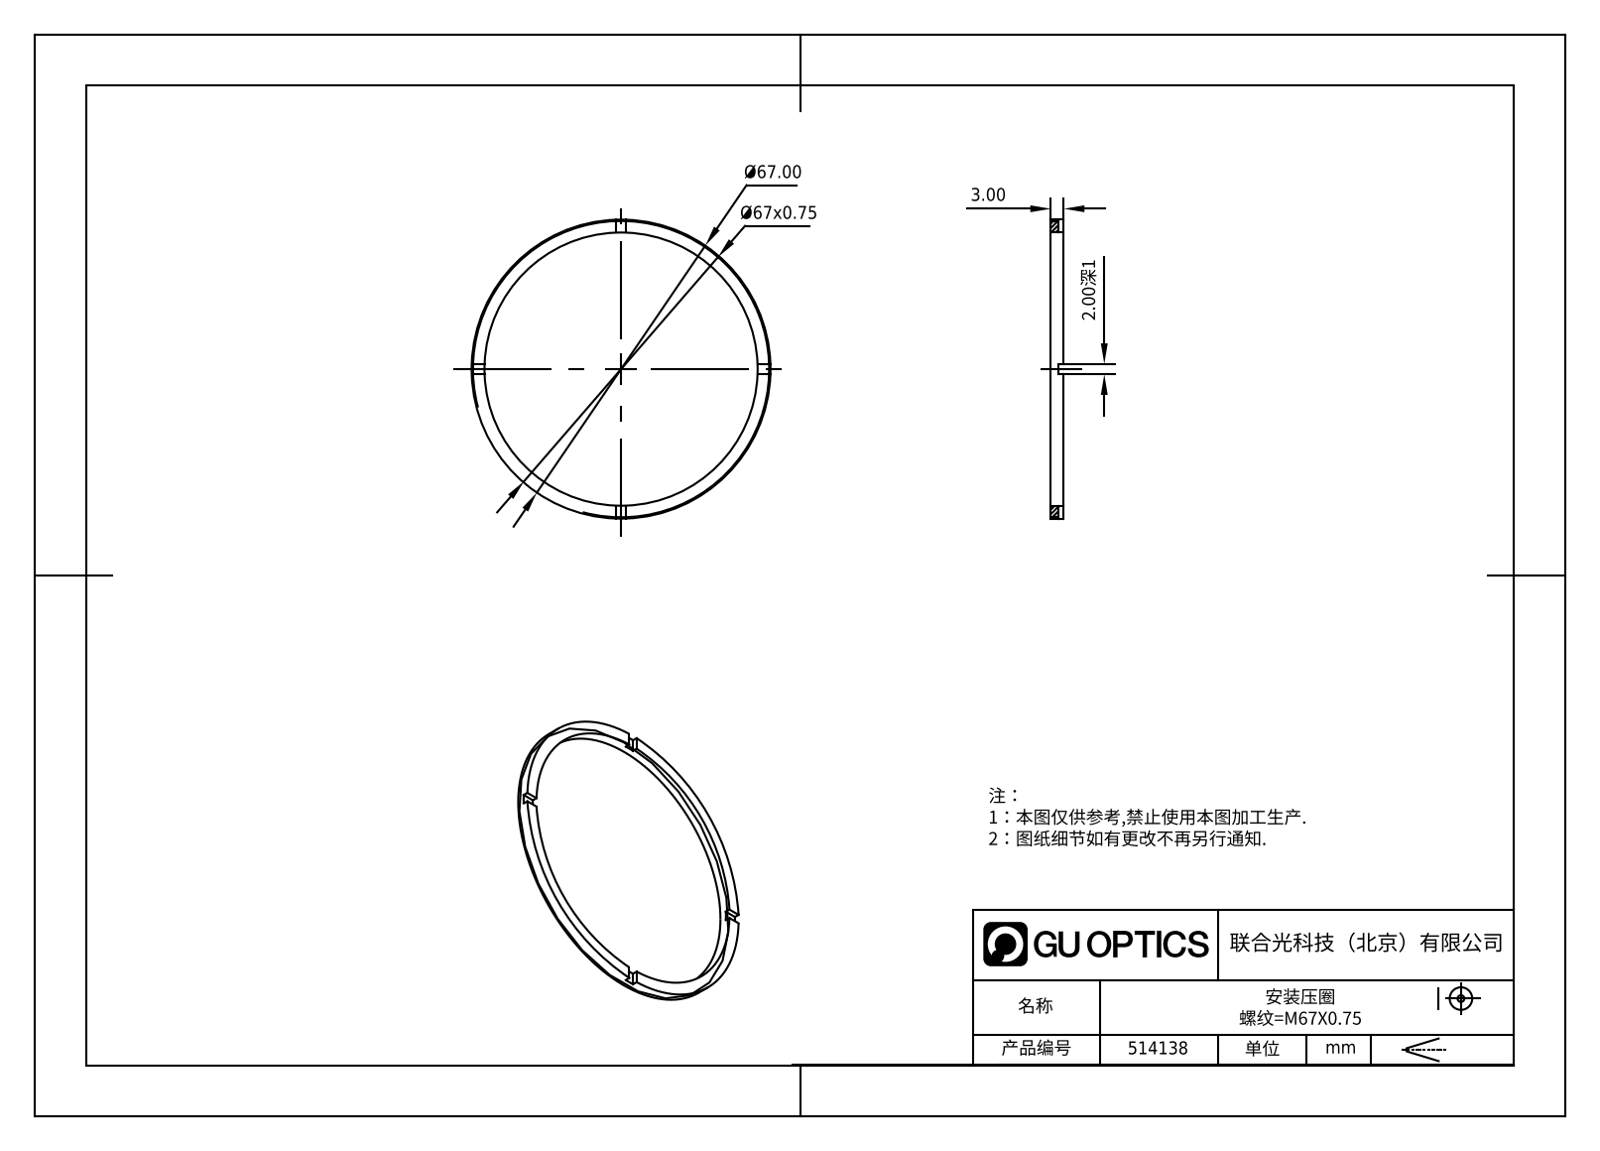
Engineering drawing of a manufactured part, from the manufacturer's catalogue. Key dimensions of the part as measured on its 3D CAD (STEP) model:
Part name (STEP PRODUCT): 514138
STEP written by: SolidWorks 2020 (CONFIG_CONTROL_DESIGN)
Units: millimetres
Bodies: 1 solid, 21 faces (17 planar, 4 cylindrical, 0 other)
Overall size (bounding box): 67 × 67 × 3
Volume: 1 500 mm³ · Surface area: 2 233 mm²
Round holes (diameter × count): ⌀62 ×1
Round bosses / shafts (diameter × count): ⌀67 ×1
Main face-to-face distances: 3, 2, 1
